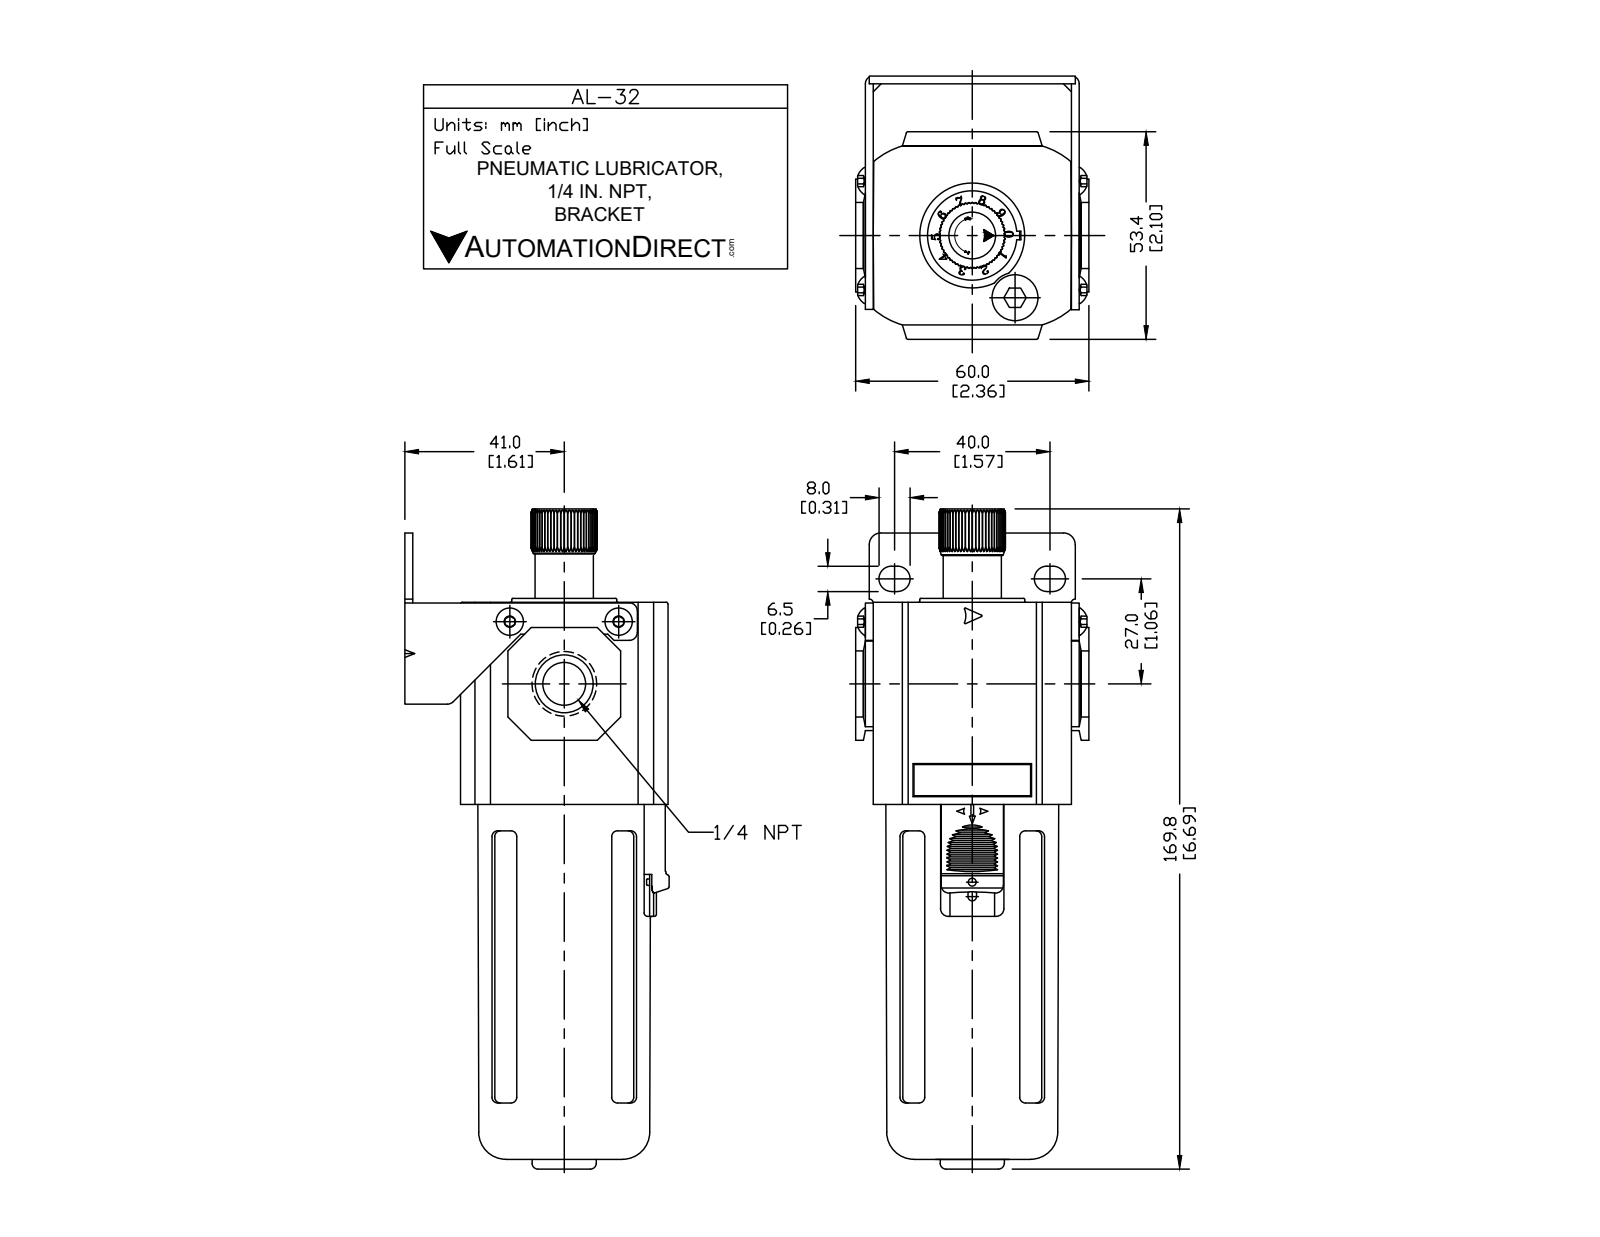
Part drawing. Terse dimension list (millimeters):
name: AL-32
written by: SolidWorks 2015 (CONFIG_CONTROL_DESIGN)
unit: mm
bodies: 7 solids, 550 faces (336 planar, 106 cylindrical, 108 other)
size: 169.8 × 67.7 × 60
volume: 206 827 mm³; area: 58 204 mm²
holes: 2× ⌀3.4, 1× ⌀11.13, 1× ⌀35.99, 1× ⌀44.8
bosses: 1× ⌀44.47, 1× ⌀26, 1× ⌀16.5, 1× ⌀15
rounds: 16× R2.2, 8× R2, 4× R0.3, 4× R3.25, 4× R20, 3× R0.2, 2× R1, 2× R3
face distances: 2, 53, 2.5, 12.3, 67.7, 65.7, 14.3, 53.4, 51, 55.5
hole spacings: 21.06, 21.46, 28
